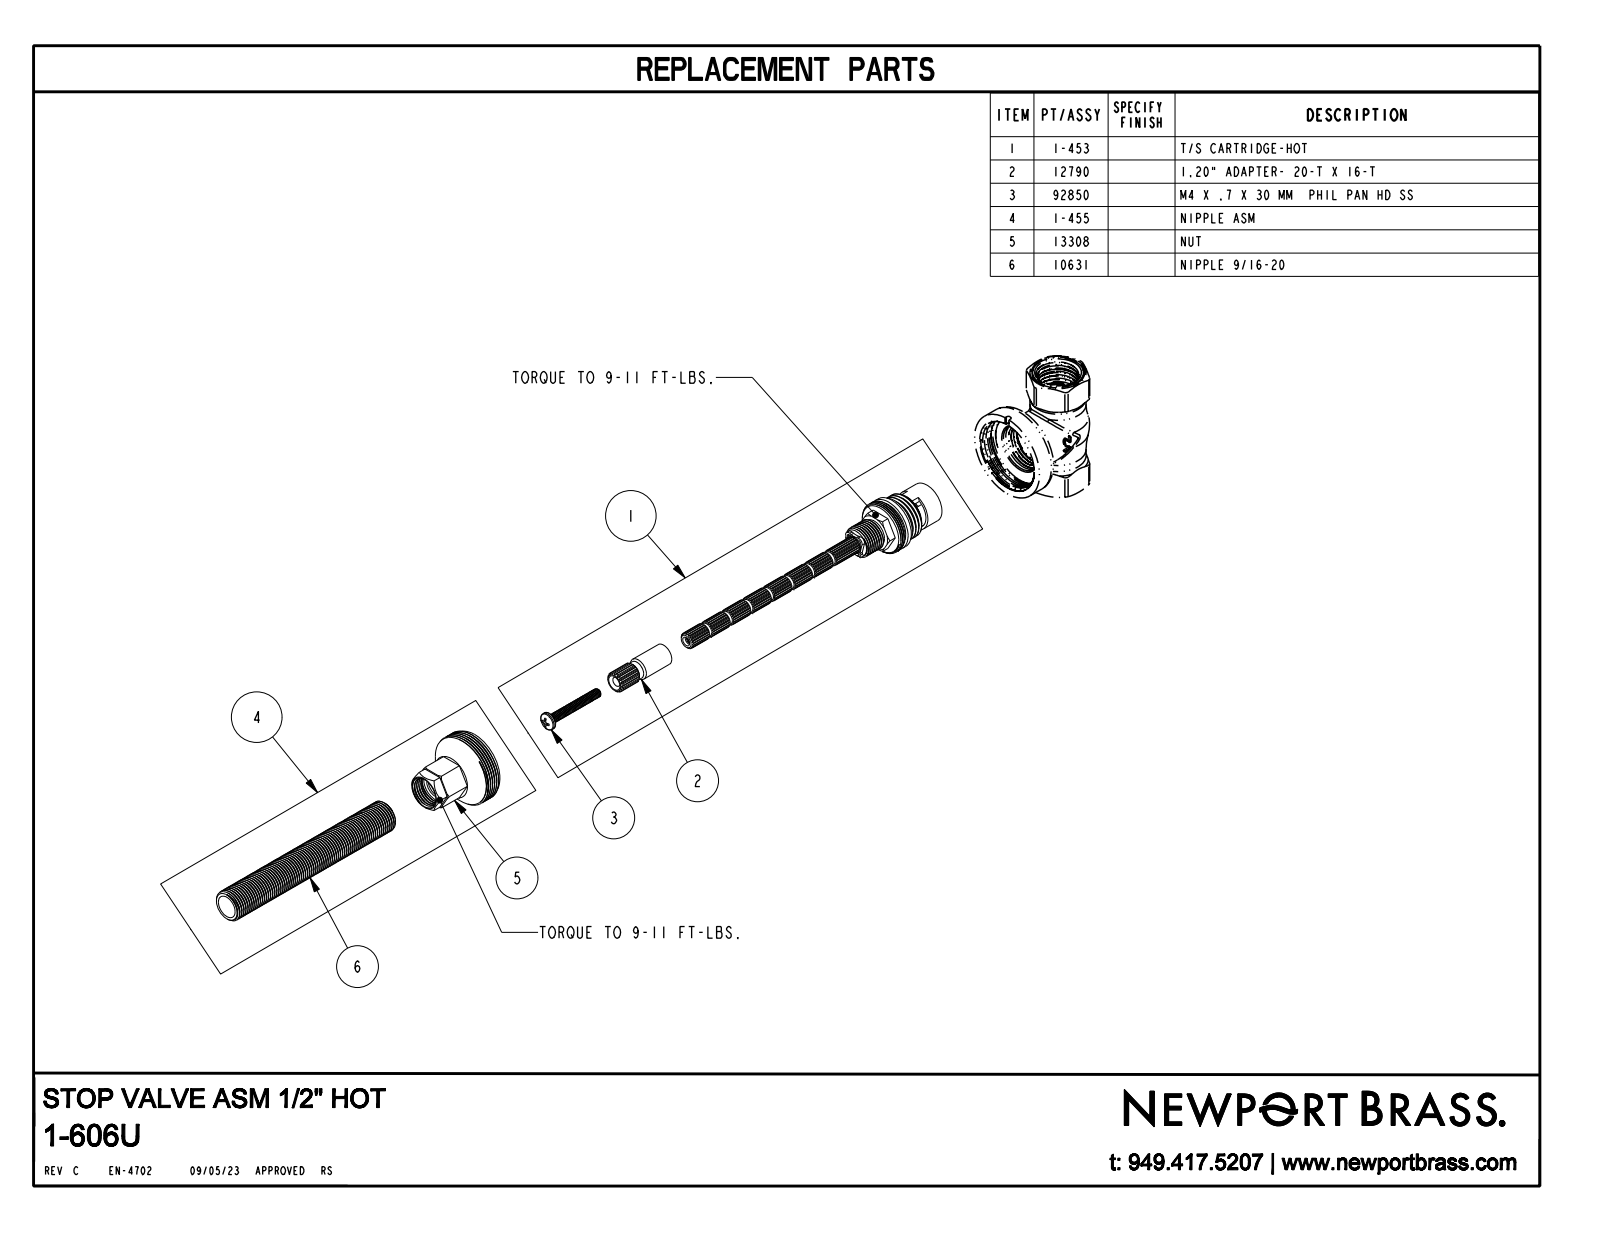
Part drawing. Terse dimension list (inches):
name: 1-606U
written by: CREO PARAMETRIC BY PTC INC, 2018400 (AUTOMOTIVE_DESIGN)
unit: in
bodies: 1 solid, 719 faces (226 planar, 352 cylindrical, 141 other)
size: 7.225 × 2.283 × 1.575
volume: 4.277 in³; area: 28.7 in²
holes: 1× ⌀0.172, 1× ⌀0.33
bosses: 1× ⌀1.575, 1× ⌀1.291, 1× ⌀0.965, 1× ⌀0.563, 1× ⌀0.391, 1× ⌀0.325, 1× ⌀0.315, 1× ⌀0.157
rounds: 1× R0.137, 1× R0.164, 1× R0.185, 1× R0.46, 1× R0.557
face distances: 0.992, 2.283, 0.669, 0.023, 0.646, 0.807, 1.476, 0.624, 0.415, 0.146
